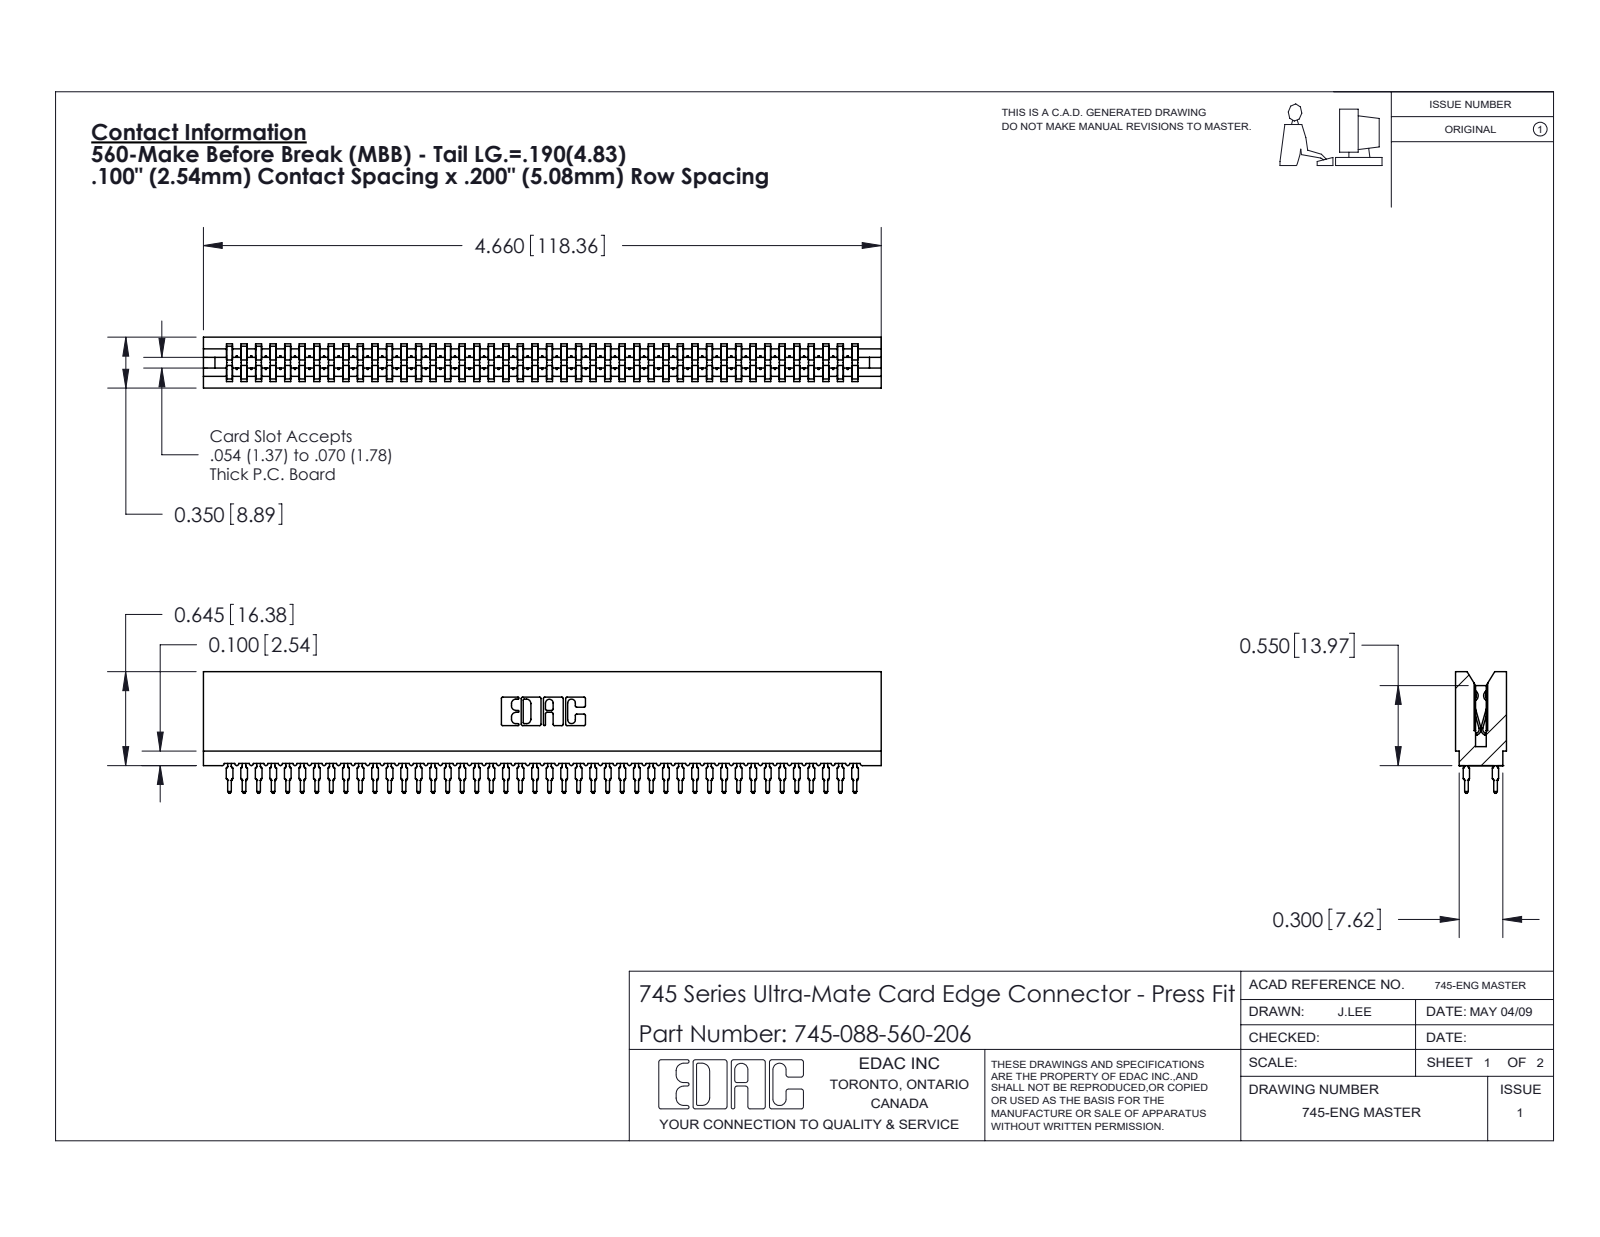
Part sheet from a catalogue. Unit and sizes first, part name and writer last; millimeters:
Units: millimetres
Overall size (bounding box): 118.4 × 21.2 × 8.9
Partial cylindrical surfaces — rounded edges, fillets, slot ends (radius × count): R0.5 ×176, R0.4 ×88, R0.3 ×22, R0.1 ×8, R0.3 ×8, R0.2 ×6, R0.8 ×6, R0.7 ×3
Main face-to-face distances: 8.9, 5.1, 1.6, 7.3, 1.1, 7.7, 0.5, 6.2, 3.5, 5.4
Volume: 10 900 mm³ · Surface area: 23 720 mm²
Bodies: 89 solids, 8764 faces (4544 planar, 1932 cylindrical, 2288 other)
Part name (STEP PRODUCT): 745-088-560-206; 745 Part_Insulator Option - 06; 745-292-001_560
STEP written by: SolidWorks 2020 (CONFIG_CONTROL_DESIGN)
